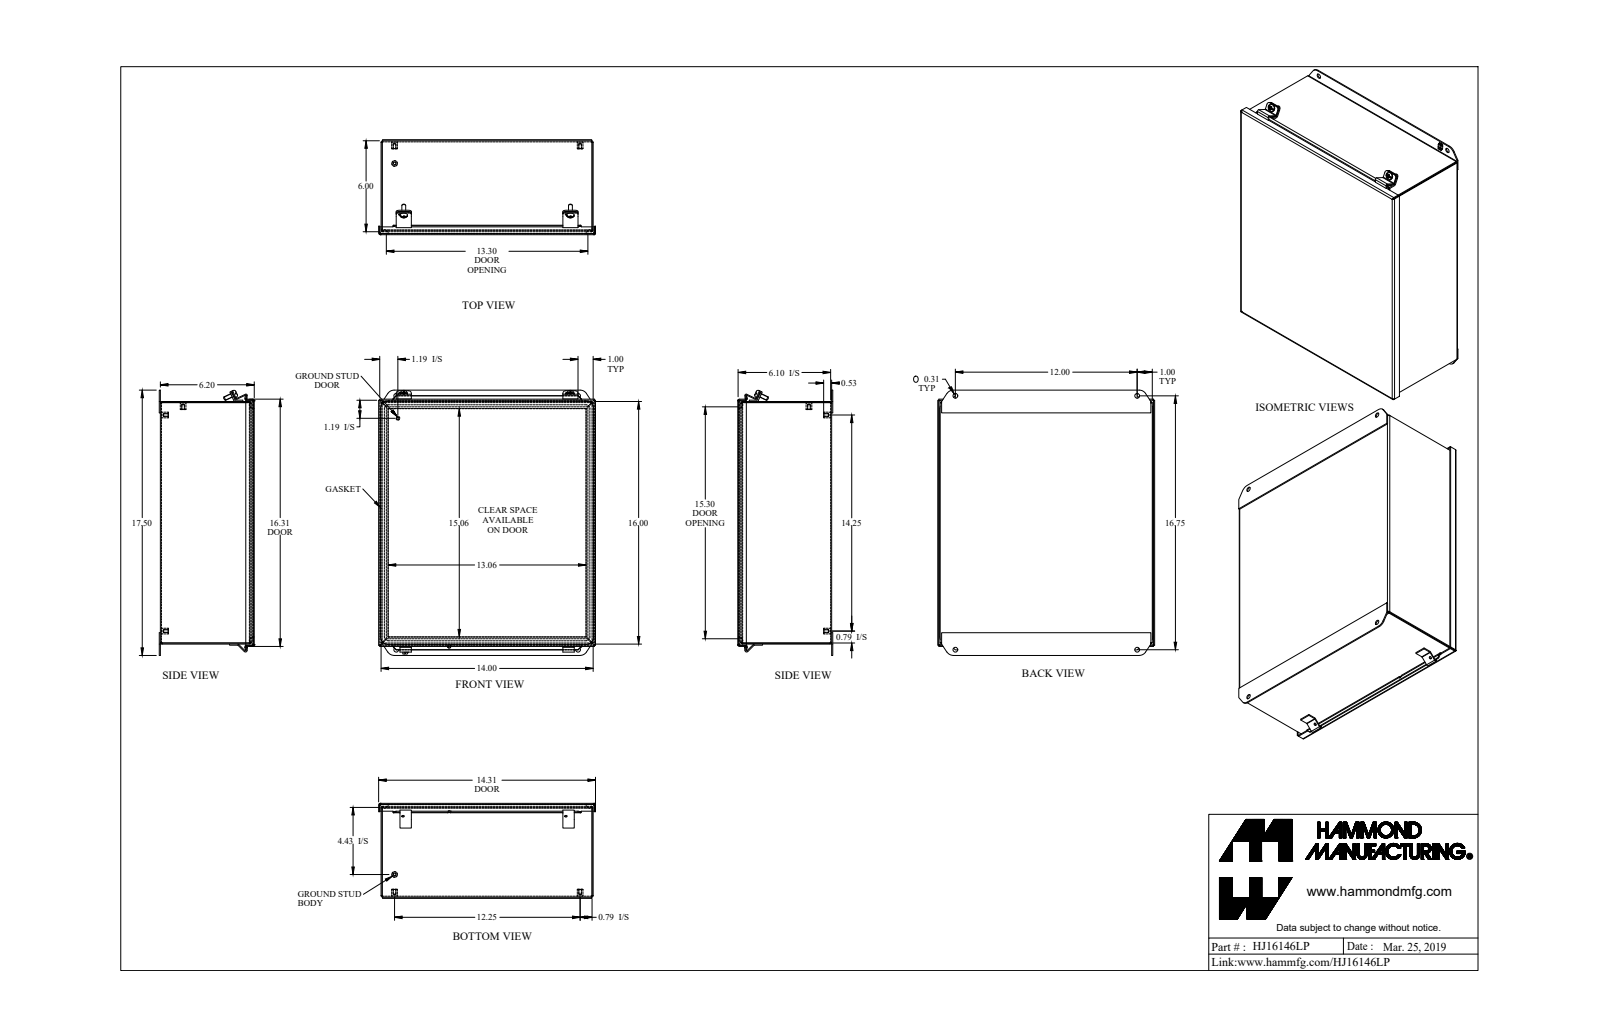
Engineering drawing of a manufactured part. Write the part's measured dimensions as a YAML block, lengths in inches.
part_name: "HJ16146LP"
step_written_by: "SolidWorks 2018 (AUTOMOTIVE_DESIGN)"
units: inches
bodies: {solids: 19, faces: 627, planar: 341, cylindrical: 160, other: 126}
overall_size: [17.5, 14.312, 6.269]
volume: 71.05
surface_area: 1967
round_holes:
  - {diameter: 0.156, count: 5}
  - {diameter: 0.313, count: 4}
  - {diameter: 0.156, count: 2}
  - {diameter: 0.213, count: 2}
round_bosses_or_shafts:
  - {diameter: 0.375, count: 5}
  - {diameter: 0.25, count: 3}
  - {diameter: 0.48, count: 2}
  - {diameter: 0.188, count: 1}
partial_cylinders:
  - {radius: 0.036, count: 16}
  - {radius: 0.108, count: 16}
  - {radius: 0.25, count: 16}
  - {radius: 0.141, count: 4}
  - {radius: 0.188, count: 4}
  - {radius: 0.499, count: 4}
  - {radius: 0.5, count: 4}
  - {radius: 0.01, count: 2}
face_to_face_distances: [0.072, 6.125, 6.197, 6.053, 13.928, 15.928, 13.856, 14, 16, 15.856]
hole_center_spacings: [12, 12.25, 14.25, 16.75, 18.792, 20.605, 1.239, 1.243]
